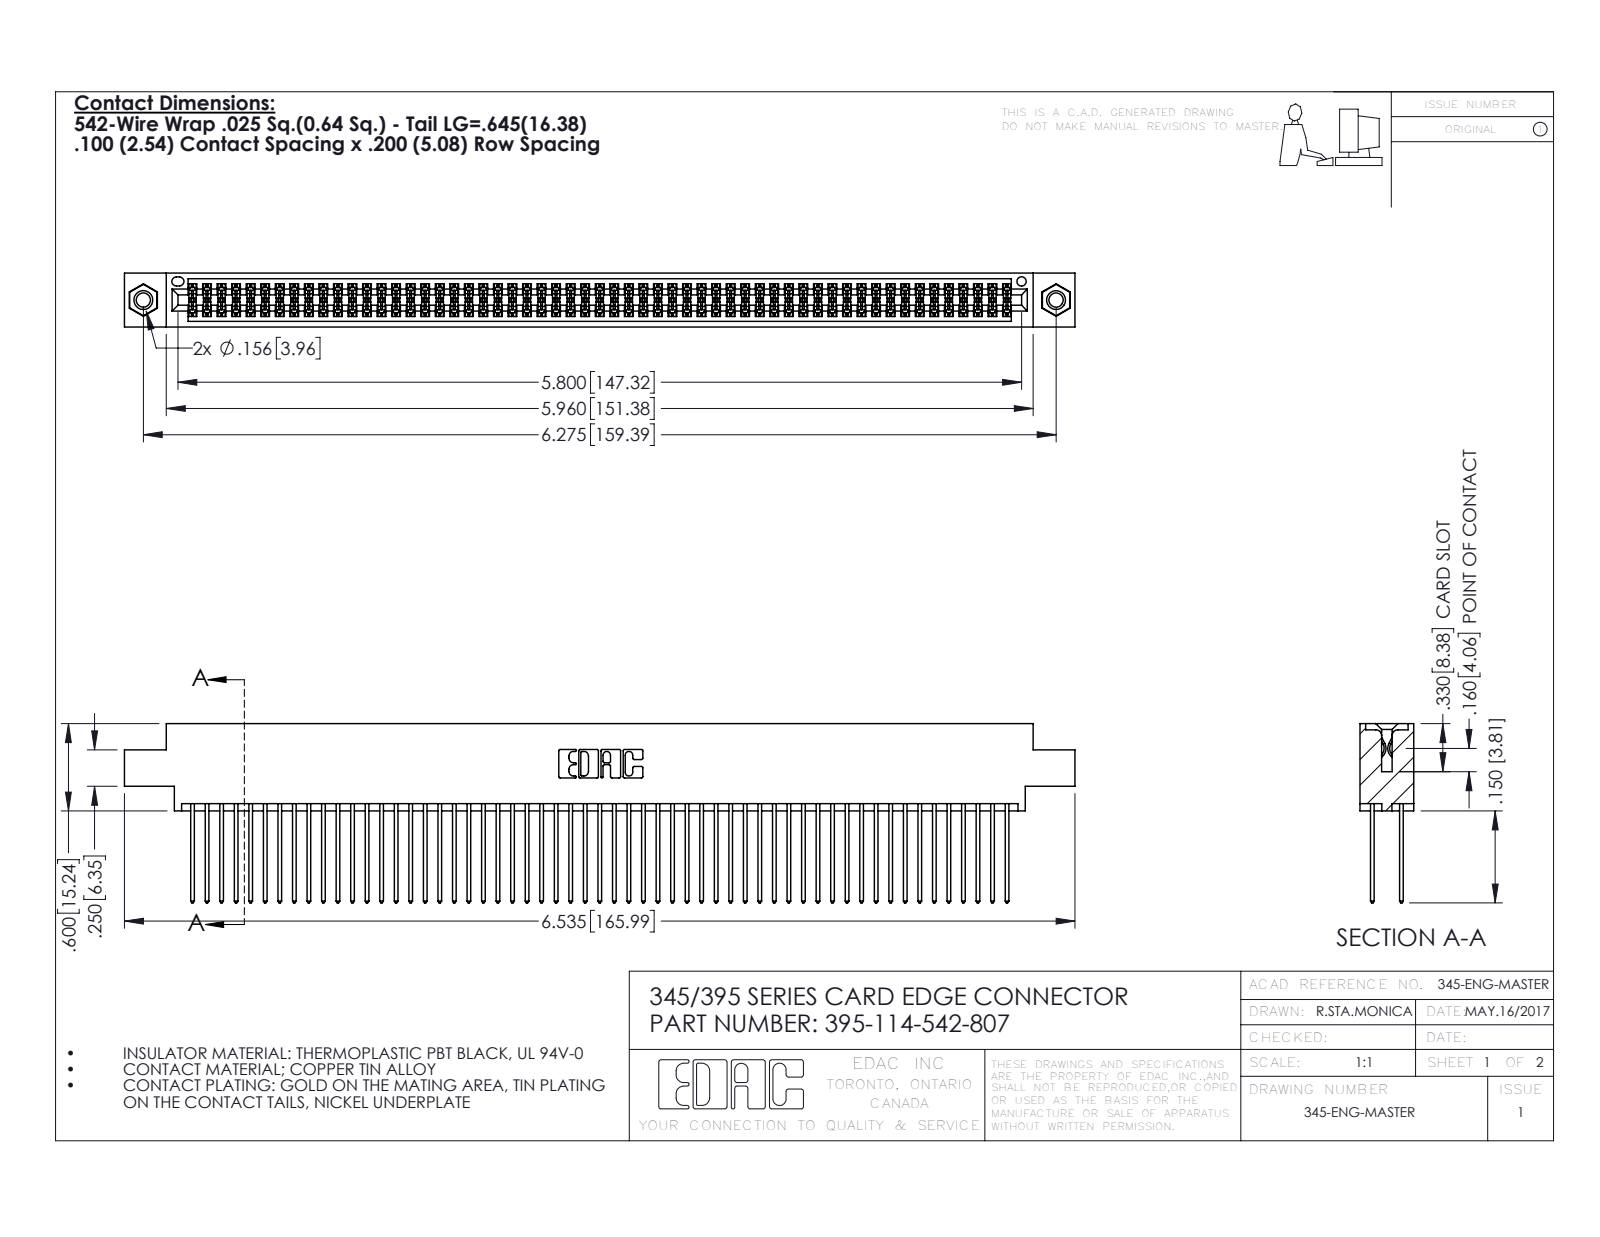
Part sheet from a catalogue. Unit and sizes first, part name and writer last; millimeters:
Units: millimetres
Overall size (bounding box): 166 × 31.3 × 9.4
Round holes (diameter × count): ⌀2.5 ×2, ⌀3.2 ×2, ⌀4 ×2, ⌀1.6 ×1
Round bosses / shafts (diameter × count): ⌀3.9 ×2
Partial cylindrical surfaces — rounded edges, fillets, slot ends (radius × count): R0.2 ×171, R0.3 ×114, R0.3 ×22, R0.2 ×6, R0.8 ×6, R0.7 ×3, R0.4 ×2, R0.5 ×2
Main face-to-face distances: 1.8, 7.6, 5.1, 2.5, 6.9, 0.6, 9.4, 5.7, 4.4, 3.8
Hole centre spacings: 6.9, 153.4, 159.4
Volume: 16 670 mm³ · Surface area: 27 580 mm²
Bodies: 117 solids, 5890 faces (3878 planar, 1996 cylindrical, 16 other)
Part name (STEP PRODUCT): 345-250-001_345-250-005-103; 395-114-542-807; 345 Part_0.170 Offset - 0.156 Dia-TI; 345-292-001_345-293-142
STEP written by: SolidWorks 2016 (CONFIG_CONTROL_DESIGN)
